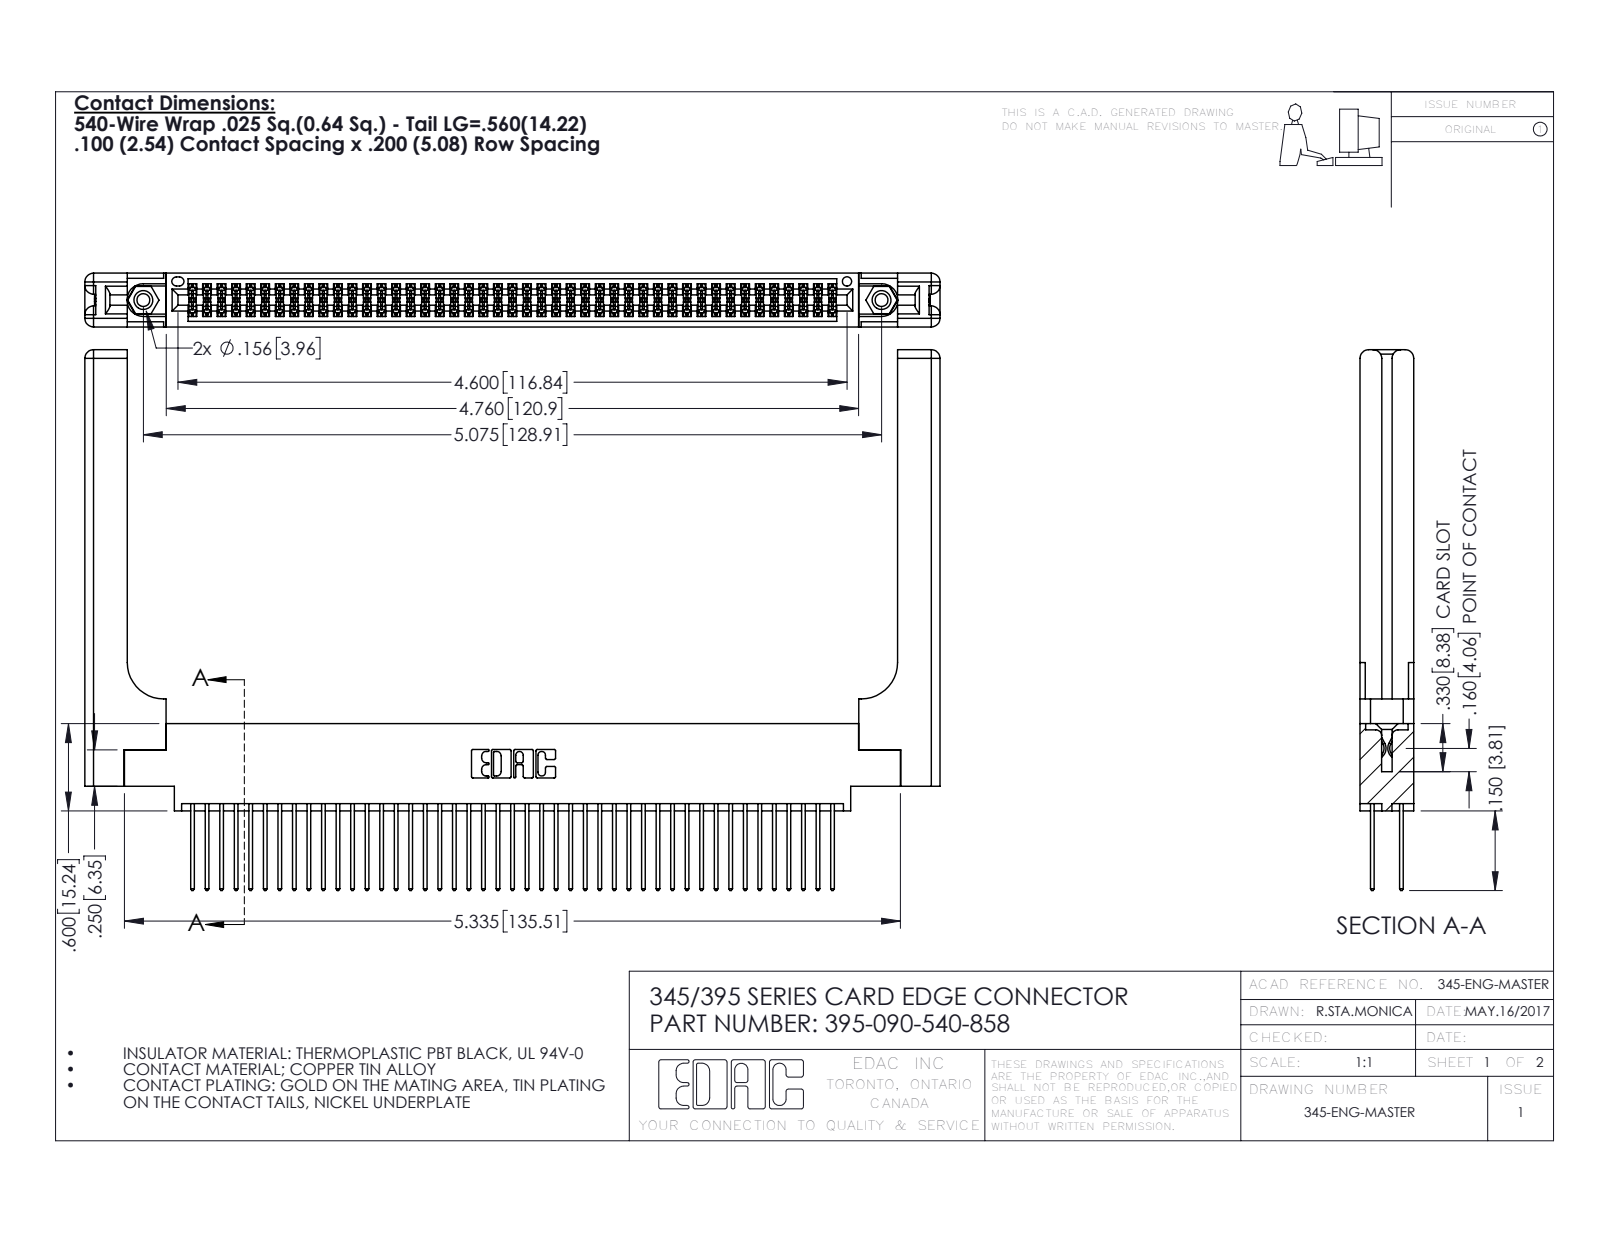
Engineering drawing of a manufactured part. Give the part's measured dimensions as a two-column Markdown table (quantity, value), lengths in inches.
| quantity | value |
| --- | --- |
| part name | 345-220-058_345-220-058; 345 Part_0.170 Offset - 0.156 Dia-TH; 345-292-001_345-293-140; 345-250-001_345-250-001-102 (+1 more) |
| STEP written by | SolidWorks 2016 (CONFIG_CONTROL_DESIGN) |
| units | inches |
| bodies | 95 solids, 4886 faces (3202 planar, 1624 cylindrical, 60 other) |
| overall size | 5.879 × 3.717 × 0.37 |
| volume | 1.418 in³ |
| surface area | 44.43 in² |
| round holes (diameter × count) | 0.089 × 2, 0.125 × 2, 0.156 × 2, 0.064 × 1 |
| round bosses / shafts (diameter × count) | 0.155 × 2 |
| partial cylindrical surfaces (radius × count) | 0.006 × 135, 0.01 × 90, 0.01 × 22, 0.06 × 16, 0.007 × 6, 0.031 × 6, 0.026 × 3, 0.014 × 2 |
| main face-to-face distances | 0.072, 0.298, 0.37, 0.098, 0.272, 0.025, 0.2, 0.225, 0.175, 0.148 |
| hole center spacings | 0.27, 4.839, 5.075 |
